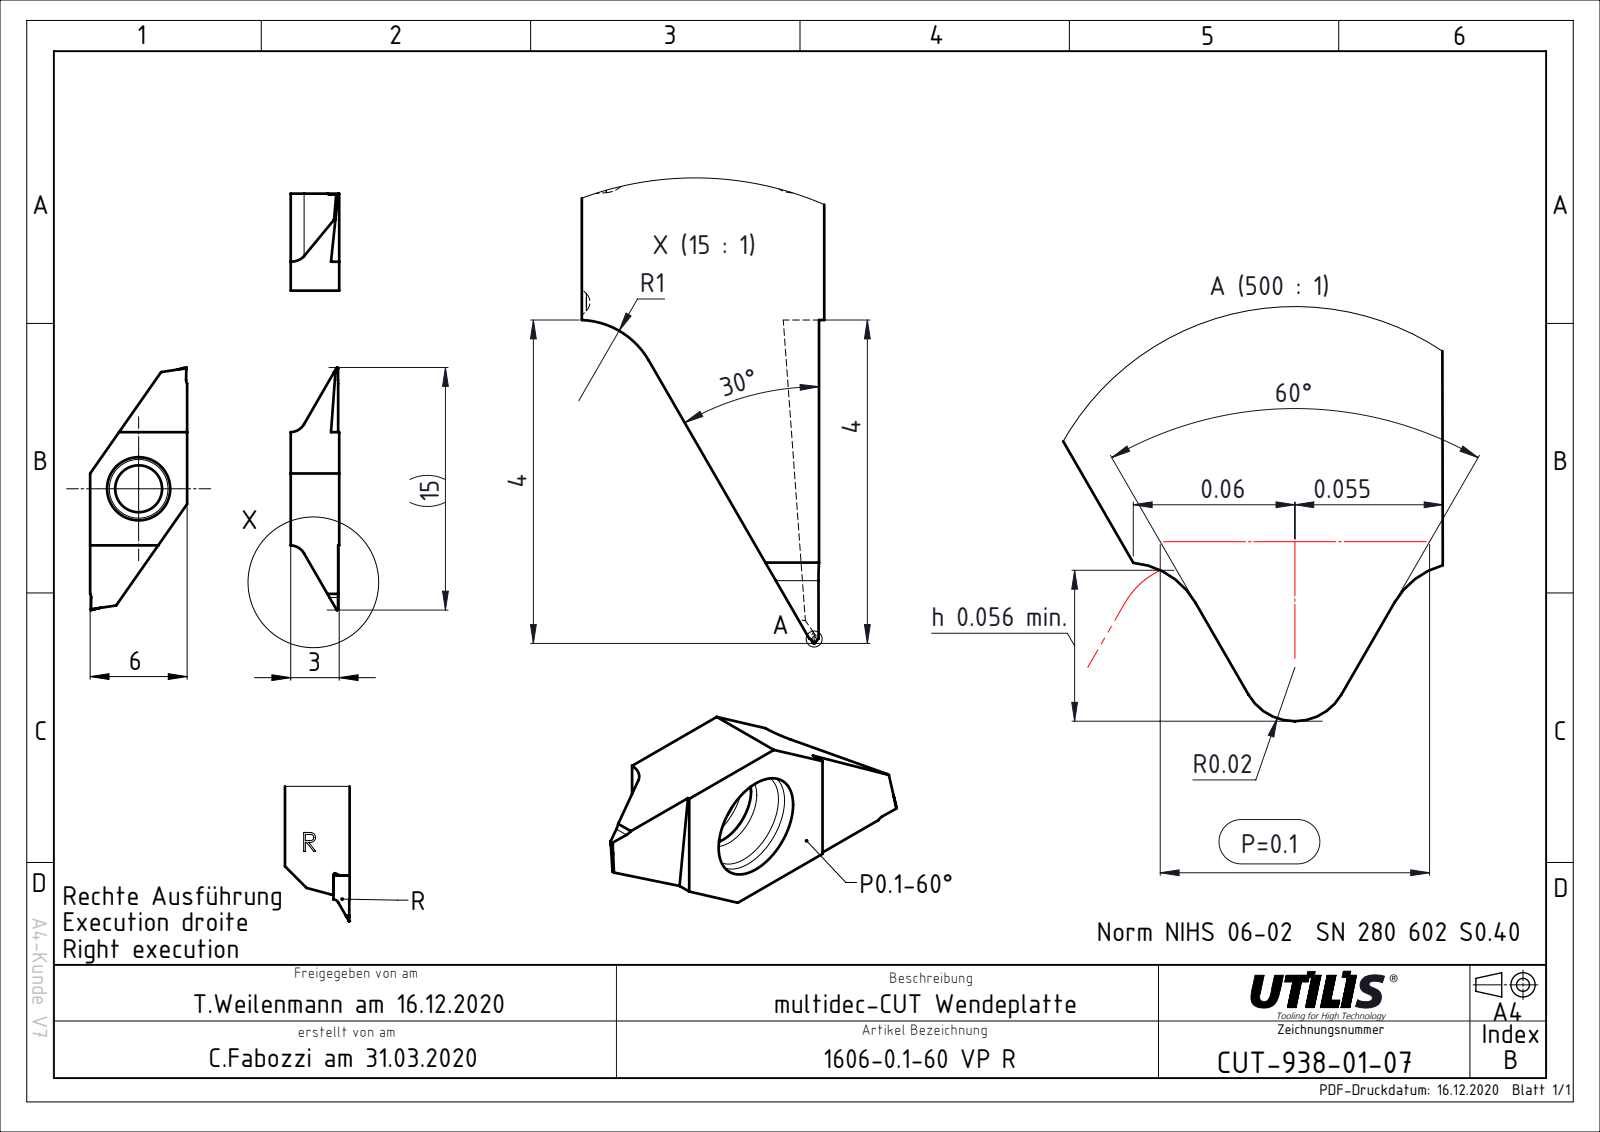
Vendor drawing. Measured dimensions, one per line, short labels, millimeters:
name: CUT-938-01; ASME Y14.5
written by: FormatWorks Professional (AP242_MANAGED_MODEL_BASED_3D_ENGINEERING_MIM_LF)
unit: mm
bodies: 1 solid, 34 faces (20 planar, 14 cylindrical, 0 other)
size: 15 × 6 × 3
volume: 124 mm³; area: 209 mm²
holes: 1× ⌀2.9
rounds: 2× R1
face distances: 6, 3, 9, 7, 12, 7.2, 7.19
